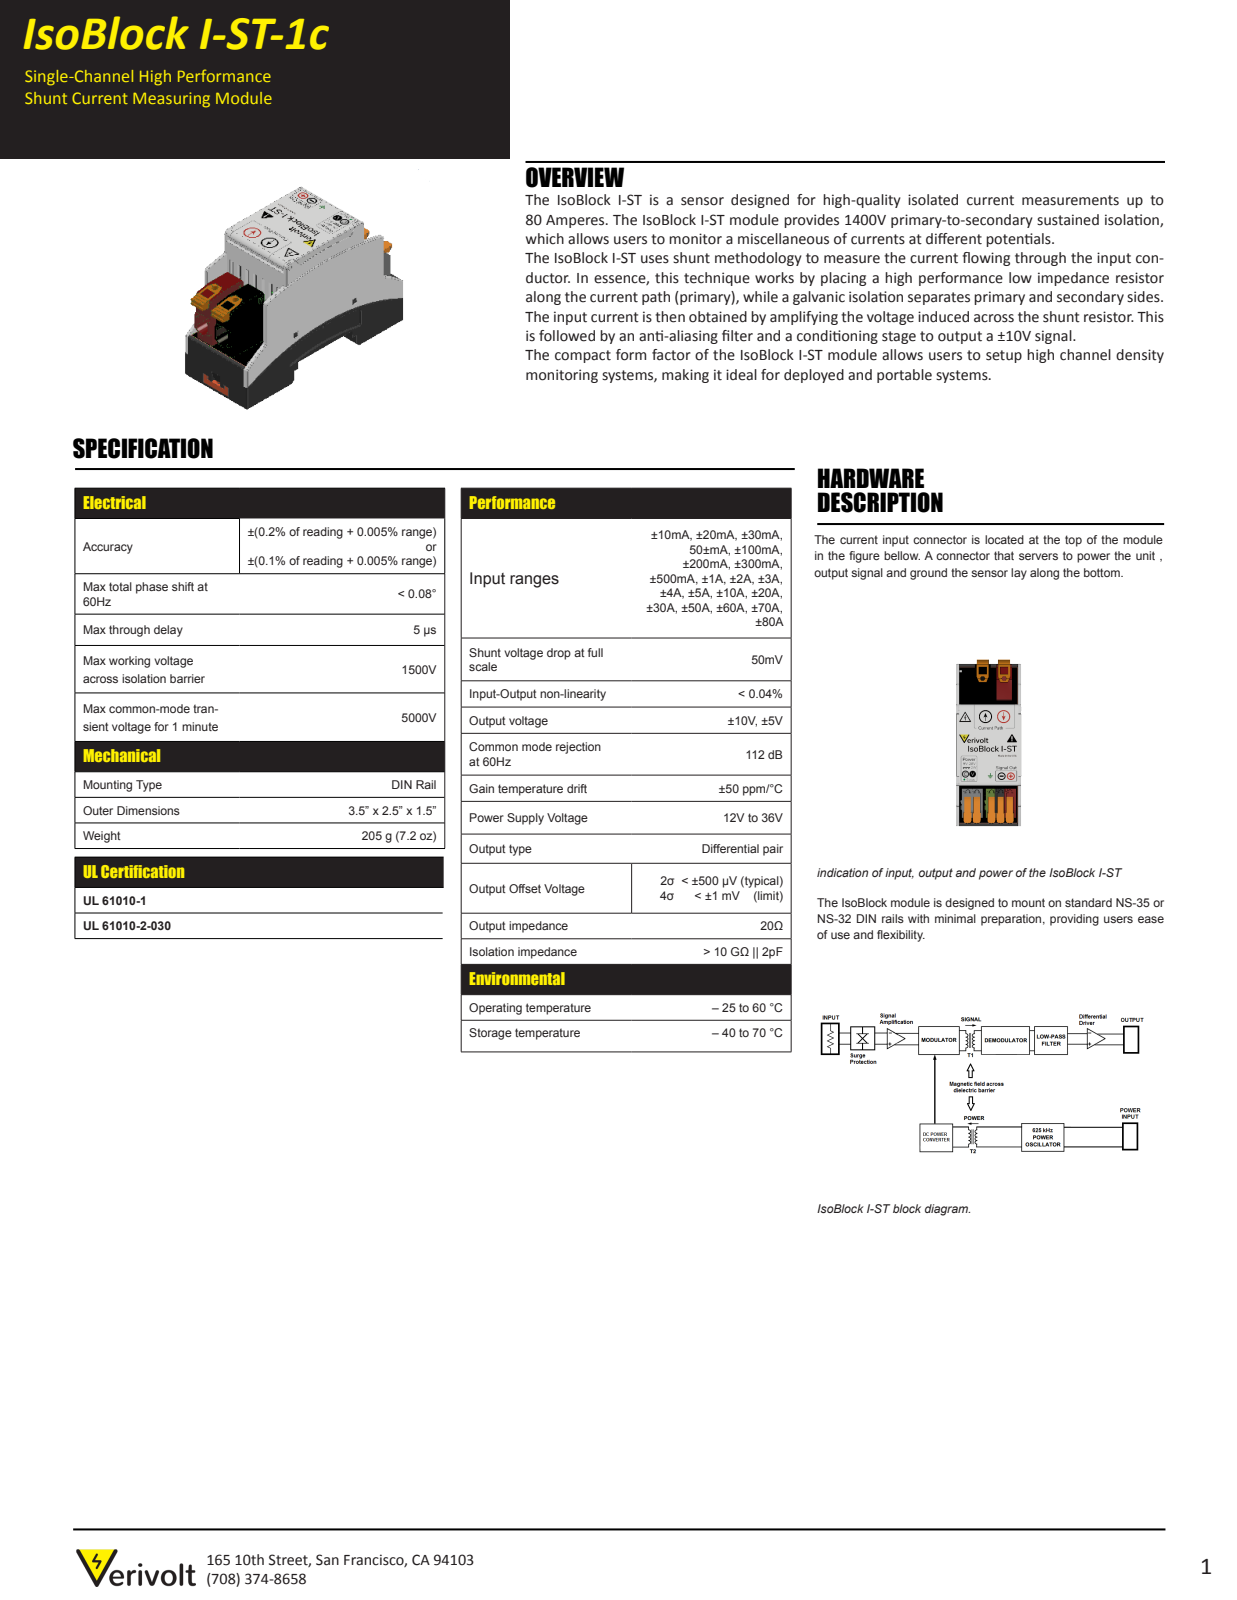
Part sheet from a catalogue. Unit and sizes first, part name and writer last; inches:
Units: inches
Overall size (bounding box): 3.533 × 2.39 × 1.402
Round holes (diameter × count): ⌀0.016 ×46, ⌀0.018 ×44, ⌀0.02 ×38, ⌀0.039 ×18, ⌀0.045 ×14, ⌀0.03 ×10, ⌀0.046 ×10, ⌀0.058 ×8, ⌀0.056 ×4, ⌀0.094 ×4, ⌀0.028 ×3, ⌀0.032 ×2
Round bosses / shafts (diameter × count): ⌀0.12 ×2, ⌀0.055 ×1
Partial cylindrical surfaces — rounded edges, fillets, slot ends (radius × count): R0.02 ×72, R0.175 ×12, R0.047 ×5, R0.059 ×5, R0.03 ×4, R0.07 ×4, R0.012 ×2, R0.031 ×2
Main face-to-face distances: 0.049, 1.303, 0.059, 0.071, 1.352, 0.028, 1.402, 0.098, 1.331, 0.022
Hole centre spacings: 0.1, 0.141, 0.2, 0.224, 0.3, 0.316, 0.4, 0.412
Volume: 3.318 in³ · Surface area: 110 in²
Bodies: 32 solids, 2611 faces (1965 planar, 583 cylindrical, 63 other)
Part name (STEP PRODUCT): IsoBlock I-ST-1c; BC 2TE I-ST; 2896254; BC_35.6_GEH-UT_HBUS_H.Select (+8 more)
STEP written by: Autodesk Inventor 2018 (AUTOMOTIVE_DESIGN)
